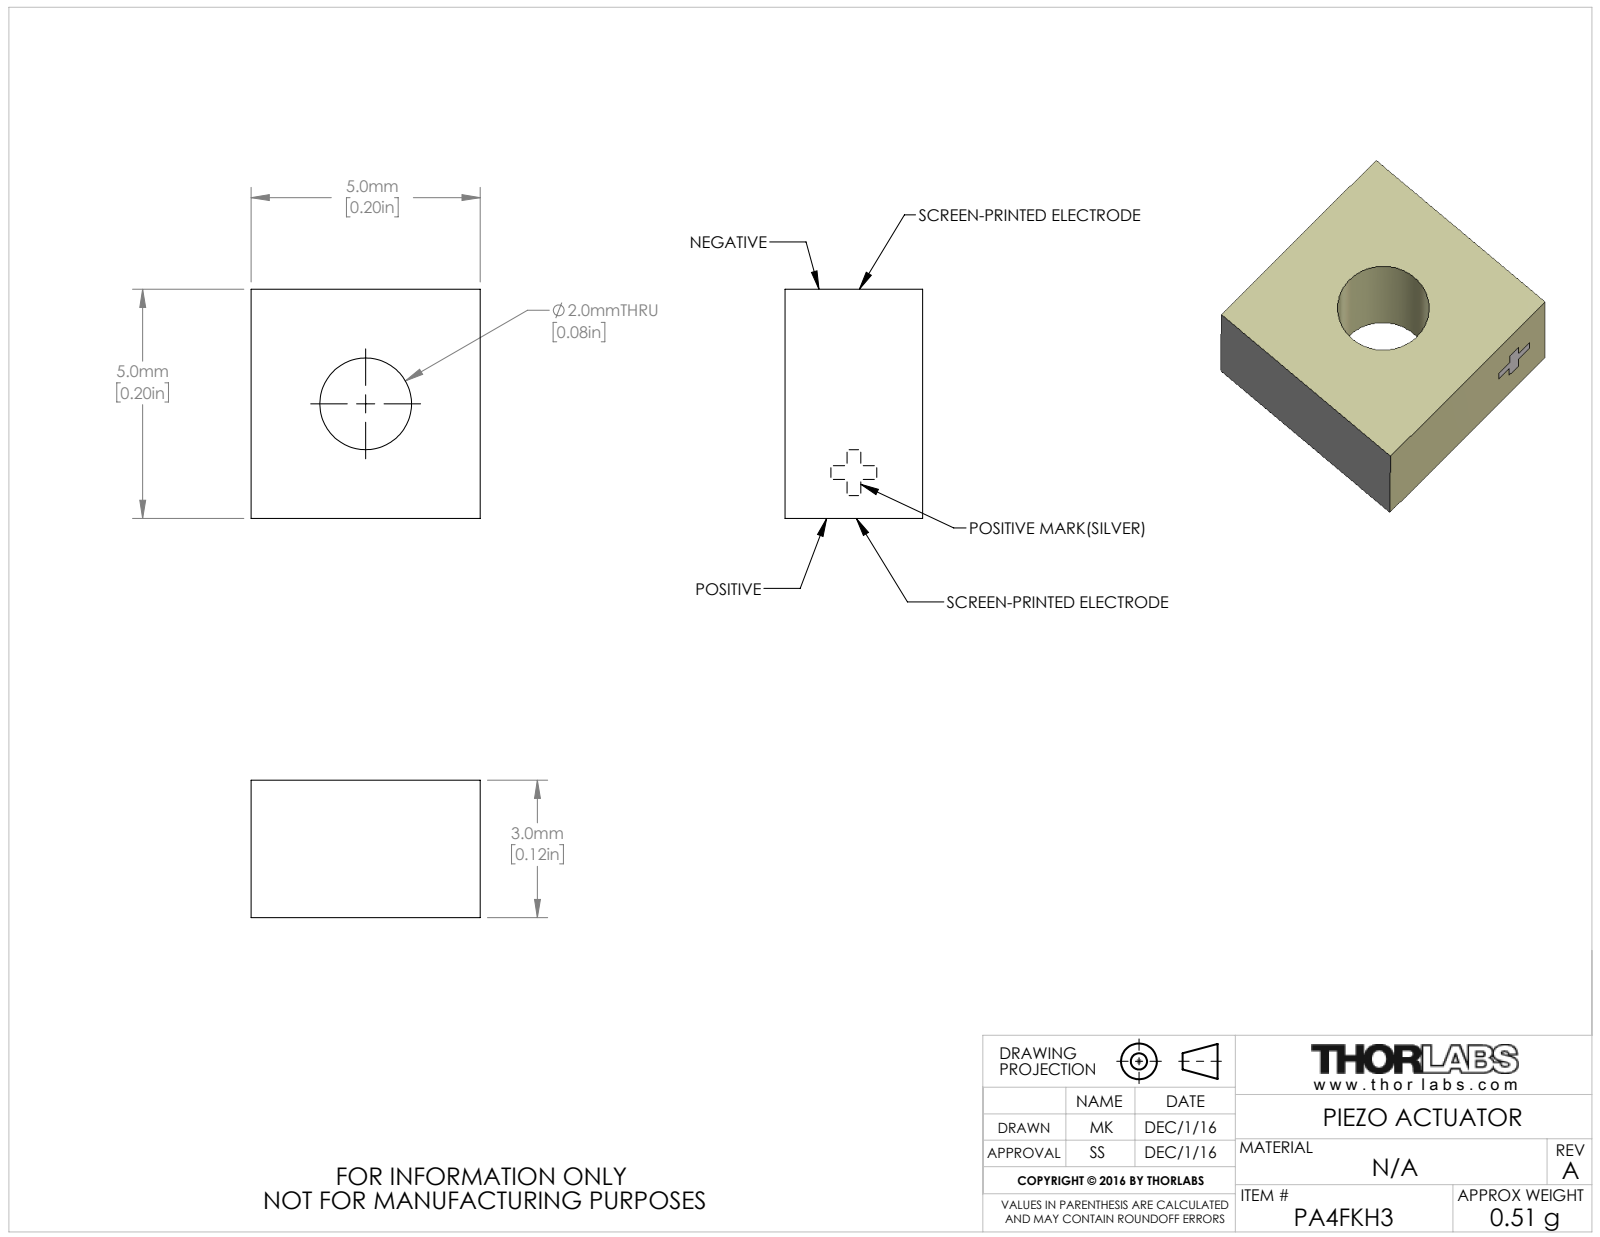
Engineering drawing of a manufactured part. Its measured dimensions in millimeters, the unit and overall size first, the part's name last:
Units: millimetres
Overall size (bounding box): 5 × 5 × 3
Round holes (diameter × count): ⌀2 ×1
Main face-to-face distances: 5, 3
Volume: 66 mm³ · Surface area: 123 mm²
Bodies: 1 solid, 9 faces (7 planar, 2 cylindrical, 0 other)
Part name (STEP PRODUCT): CTN009417
STEP written by: SolidWorks 2016 (AUTOMOTIVE_DESIGN)
